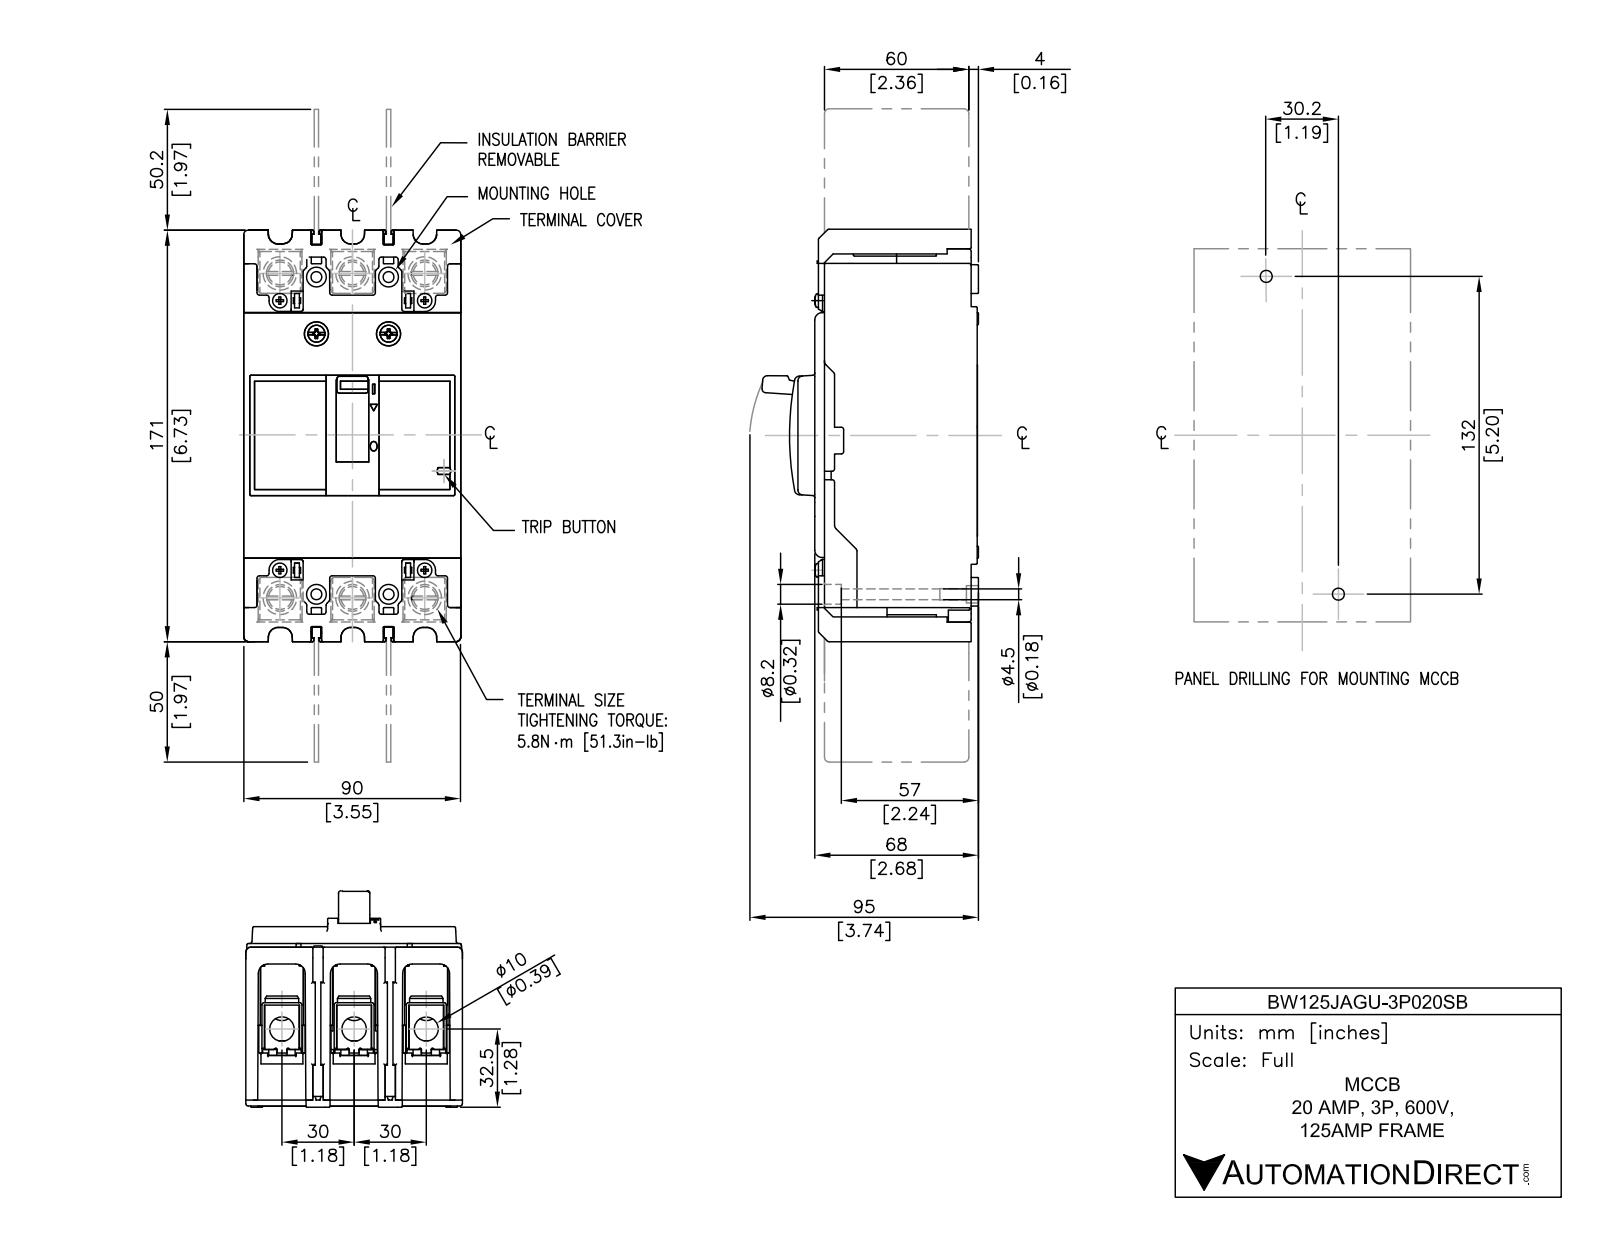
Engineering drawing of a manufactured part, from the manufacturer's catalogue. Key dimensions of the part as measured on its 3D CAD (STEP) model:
Part name (STEP PRODUCT): BW125JAGU-3P020SB
STEP written by: SolidWorks 2018 (AUTOMOTIVE_DESIGN)
Units: inches
Bodies: 14 solids, 452 faces (340 planar, 88 cylindrical, 24 other)
Overall size (bounding box): 10.197 × 3.602 × 3.543
Volume: 57.4 in³ · Surface area: 230.3 in²
Round holes (diameter × count): ⌀0.315 ×6, ⌀0.177 ×4, ⌀0.323 ×4
Round bosses / shafts (diameter × count): ⌀0.472 ×6
Partial cylindrical surfaces — rounded edges, fillets, slot ends (radius × count): R0.157 ×12, R0.079 ×6, R0.118 ×6
Main face-to-face distances: 1.181, 1.11, 1.252, 2.291, 2.433, 0.142, 3.543, 0.236, 2.402, 1.039
Hole centre spacings: 0.593, 5.289, 1.181, 1.772, 5.444, 5.546, 5.315, 2.362
